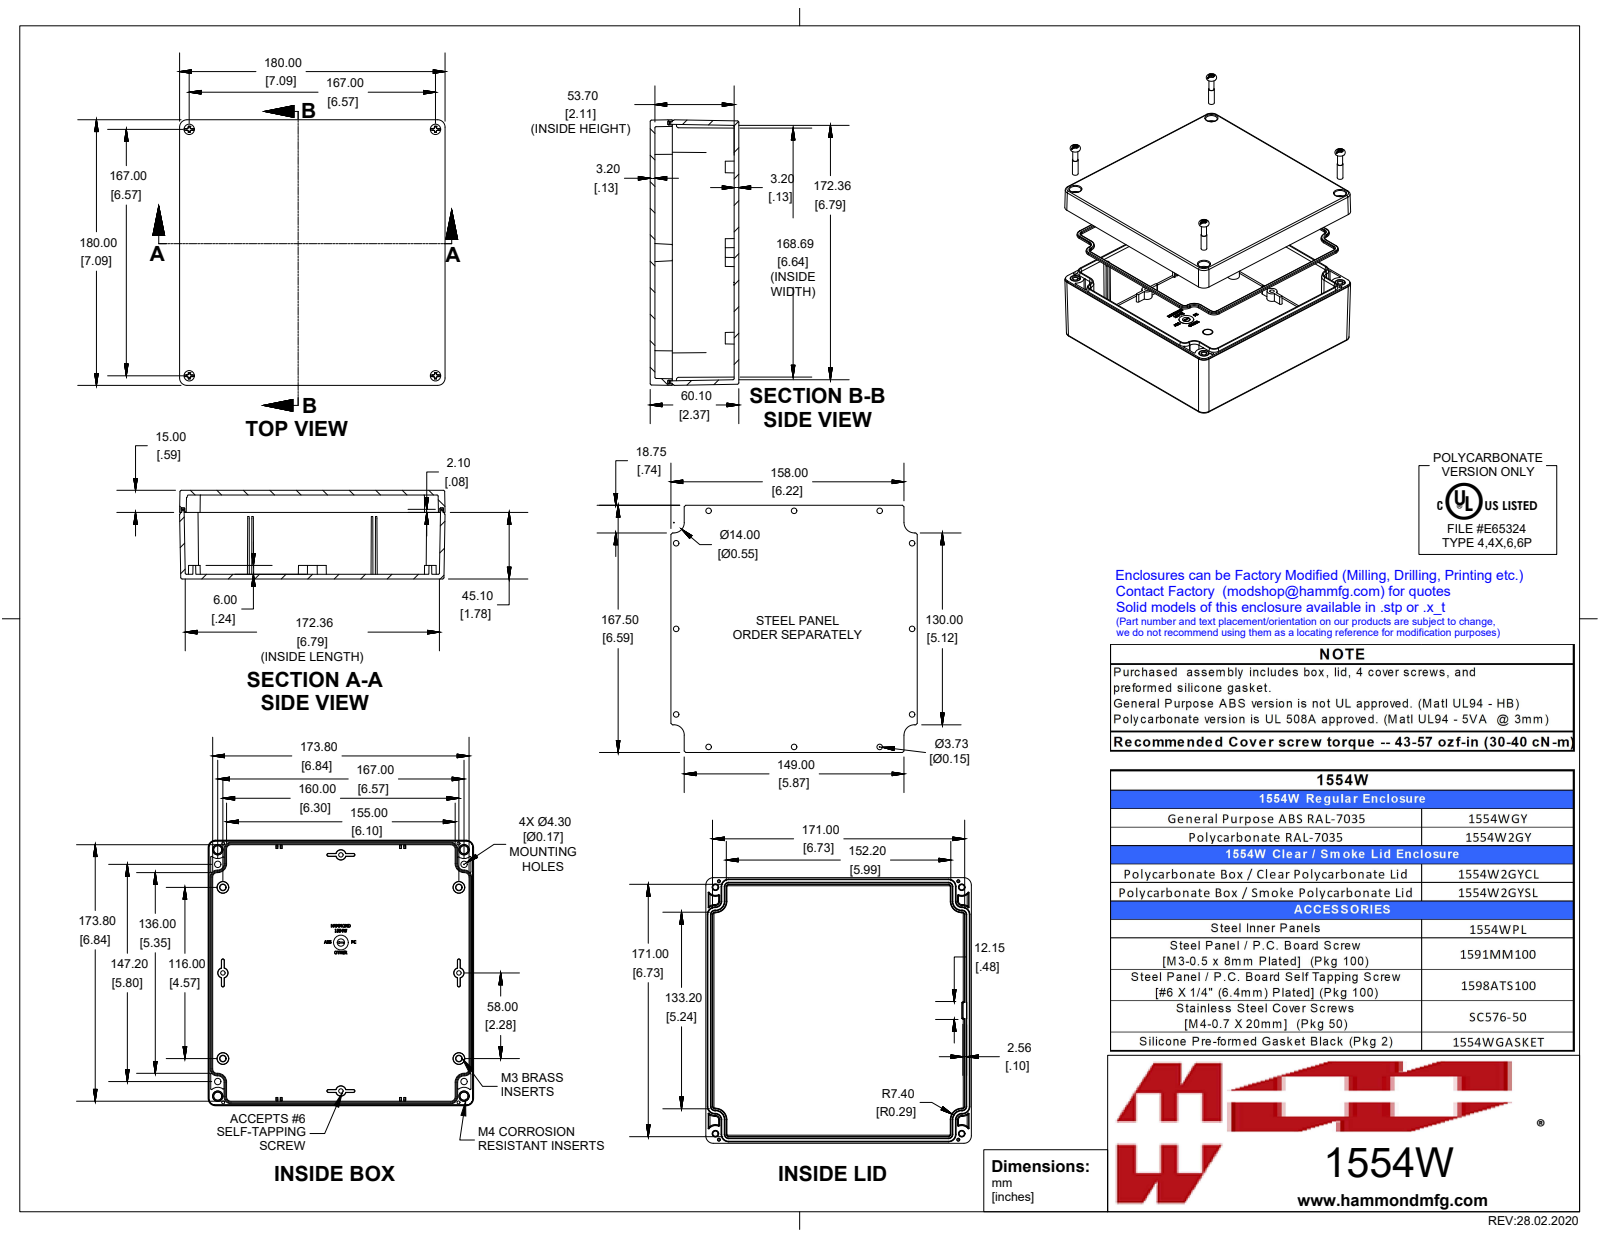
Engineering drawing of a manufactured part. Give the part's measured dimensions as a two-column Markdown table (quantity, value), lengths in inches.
| quantity | value |
| --- | --- |
| part name | 1554WGY |
| STEP written by | SolidWorks 2019 (AUTOMOTIVE_DESIGN) |
| units | inches |
| bodies | 15 solids, 1862 faces (623 planar, 374 cylindrical, 865 other) |
| overall size | 7.087 × 7.087 × 2.366 |
| volume | 21.31 in³ |
| surface area | 364.9 in² |
| round holes (diameter × count) | 0.097 × 4, 0.128 × 4, 0.181 × 4 |
| round bosses / shafts (diameter × count) | 0.25 × 4, 0.218 × 4, 0.21 × 4, 0.19 × 4, 0.154 × 4, 0.153 × 4, 0.15 × 4, 0.135 × 4 |
| partial cylindrical surfaces (radius × count) | 0.02 × 26, 0.012 × 20, 0.039 × 12, 0.031 × 10, 0.104 × 8, 0.197 × 8, 0.199 × 8, 0.118 × 4 |
| main face-to-face distances | 0.126, 2.24, 2.366, 2.114, 0.122, 6.965, 7.087, 6.909, 0.177, 6.787 |
| hole center spacings | 1.013, 5.572, 6.515, 6.575, 8.513, 4.567, 6.299, 7.781 |
